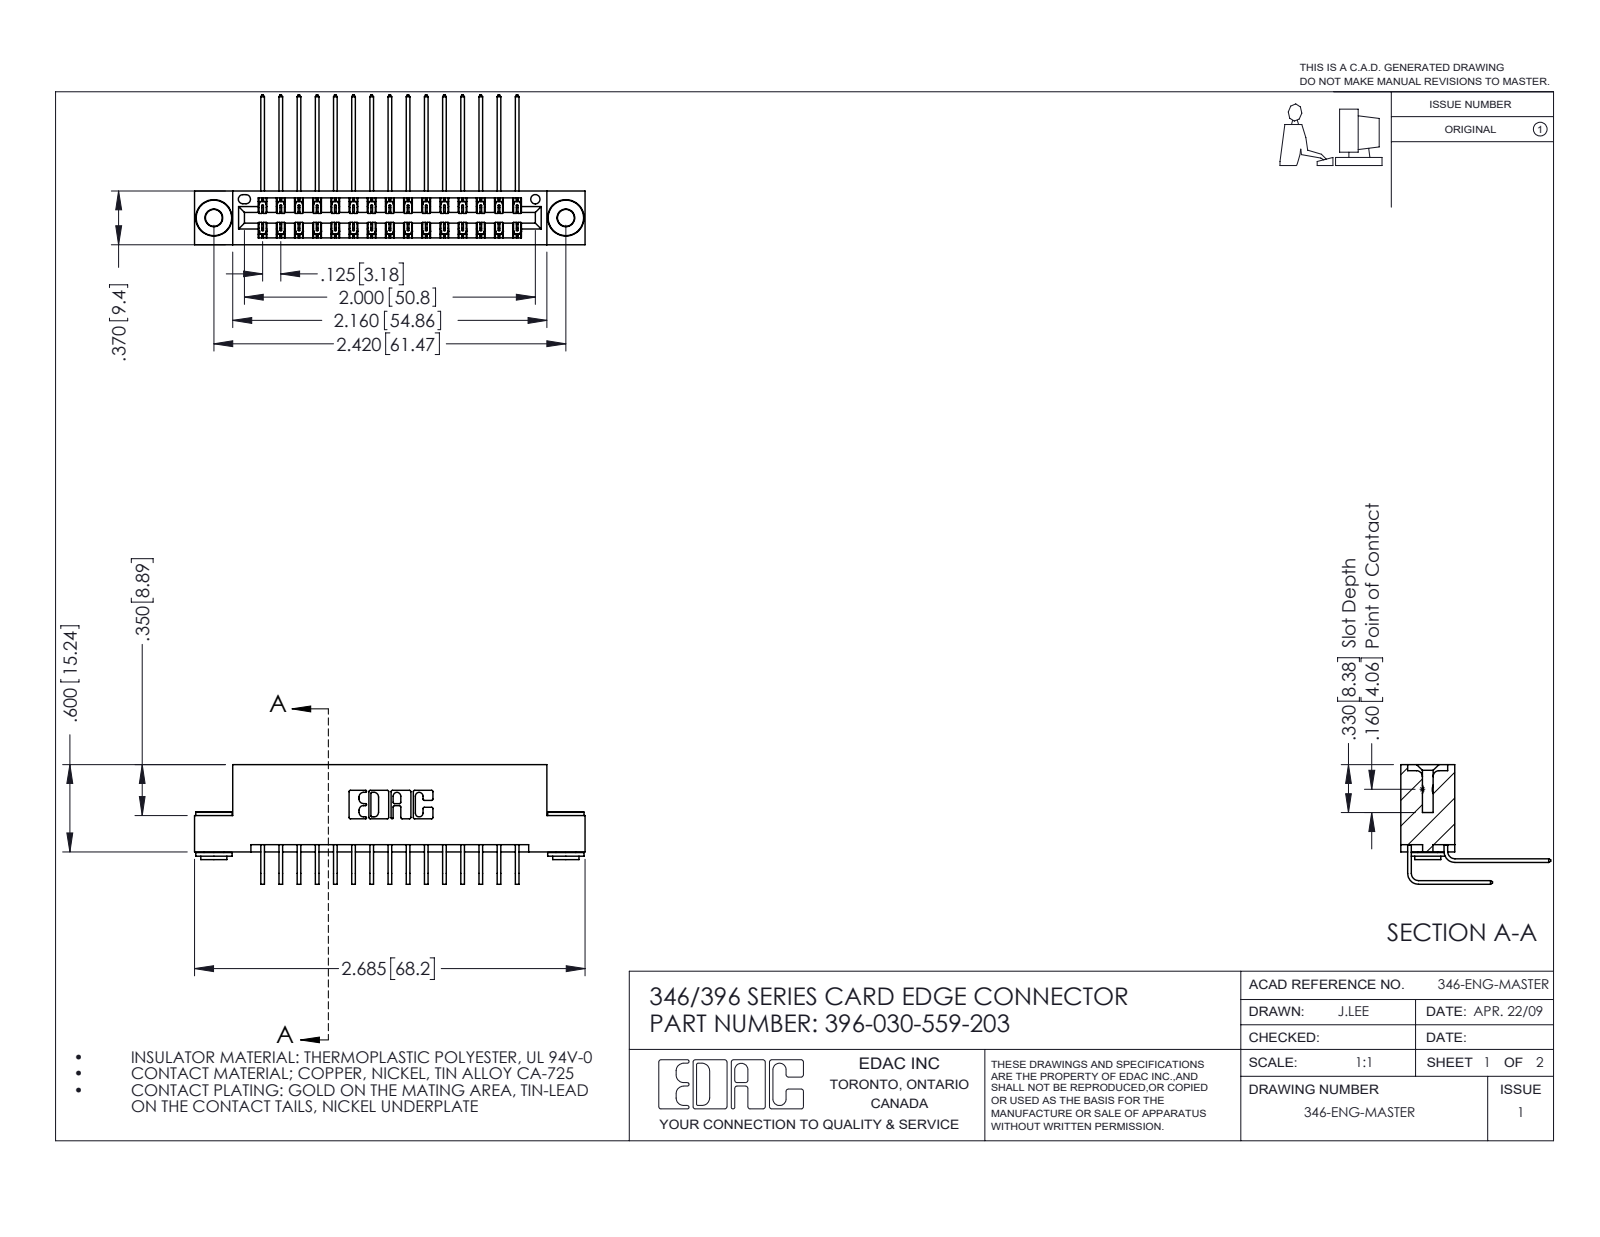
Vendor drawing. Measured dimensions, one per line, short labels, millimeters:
name: 396-030-559-203; 346 Part_Flush Mounting Lugs - 0.156 Dia-TH; 345-250-002_345-250-002-102; 345-292-001_558 559 Tail - 1 (+1 more)
written by: SolidWorks 2016 (CONFIG_CONTROL_DESIGN)
unit: mm
bodies: 33 solids, 1780 faces (1196 planar, 576 cylindrical, 8 other)
size: 68.2 × 26.2 × 20.9
volume: 6 640 mm³; area: 9 735 mm²
holes: 2× ⌀2.9, 2× ⌀4, 1× ⌀1.6
bosses: 2× ⌀6.4, 2× ⌀4.6, 2× ⌀3.5
rounds: 45× R0.2, 22× R0.3, 6× R0.2, 6× R0.8, 3× R0.7, 2× R0.4, 2× R0.6, 2× R0.6
face distances: 1.2, 8.2, 6.4, 0.6, 9.4, 1.8, 7.6, 7, 3.8, 5.6
hole spacings: 6.2, 56.2, 61.5
